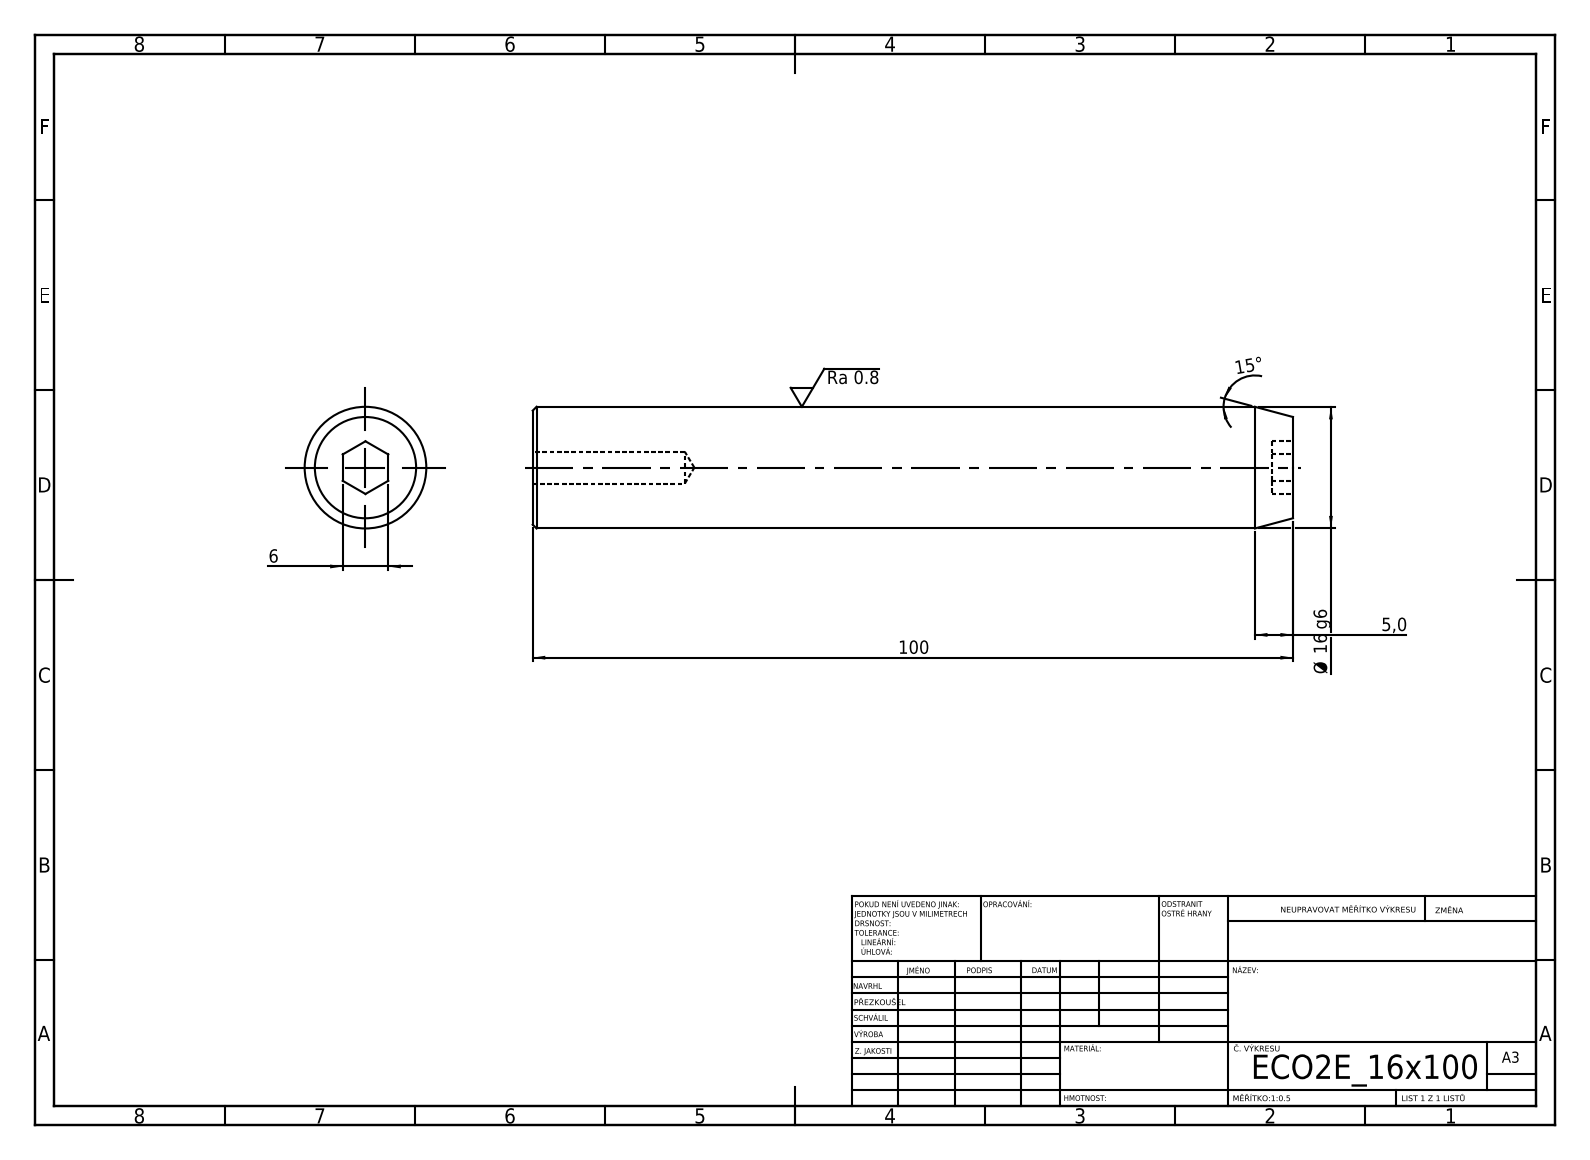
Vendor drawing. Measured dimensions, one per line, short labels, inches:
written by: SolidWorks 2019 (CONFIG_CONTROL_DESIGN)
unit: in
bodies: 1 solid, 19 faces (9 planar, 4 cylindrical, 6 other)
size: 3.937 × 0.63 × 0.63
volume: 1.194 in³; area: 8.778 in²
holes: 1× ⌀0.165
bosses: 1× ⌀0.63
face distances: 3.937, 0.11, 3.827, 0.236
